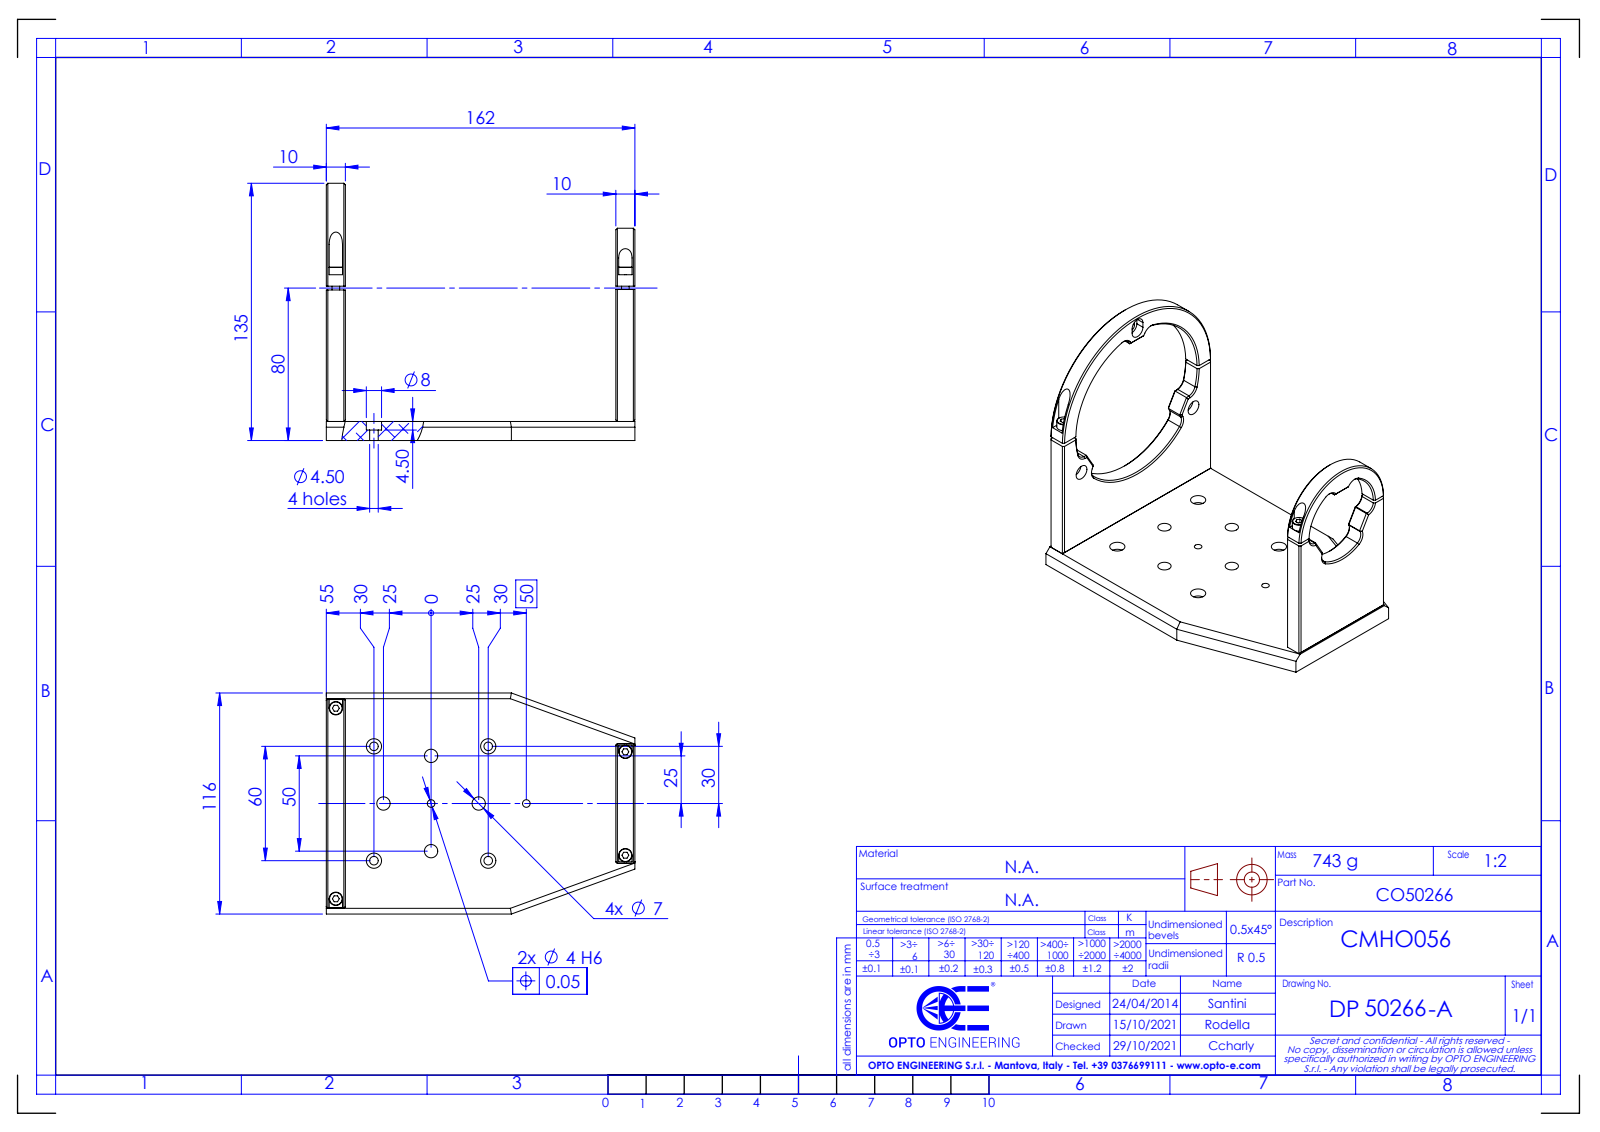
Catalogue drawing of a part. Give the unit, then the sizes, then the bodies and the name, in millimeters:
Units: millimetres
Overall size (bounding box): 162 × 135 × 116
Round holes (diameter × count): ⌀8 ×10, ⌀4.5 ×6, ⌀7 ×6, ⌀4 ×2
Round bosses / shafts (diameter × count): ⌀7 ×2, ⌀4 ×2
Partial cylindrical surfaces — rounded edges, fillets, slot ends (radius × count): R5 ×12, R2.25 ×2, R4 ×2, R23.9 ×1, R31.4 ×1, R45 ×1, R55 ×1
Main face-to-face distances: 10, 152, 162, 142, 3, 26.6, 89.4, 113, 23.6, 86.4
Hole centre spacings: 30.41, 62.65, 25, 35.36, 42.43, 50, 60, 55.9
Bodies: 0 solids, 313 faces (159 planar, 90 cylindrical, 64 other)
Part name (STEP PRODUCT): DP50266-A_CMHO056
STEP written by: SolidWorks 2021 (CONFIG_CONTROL_DESIGN)
